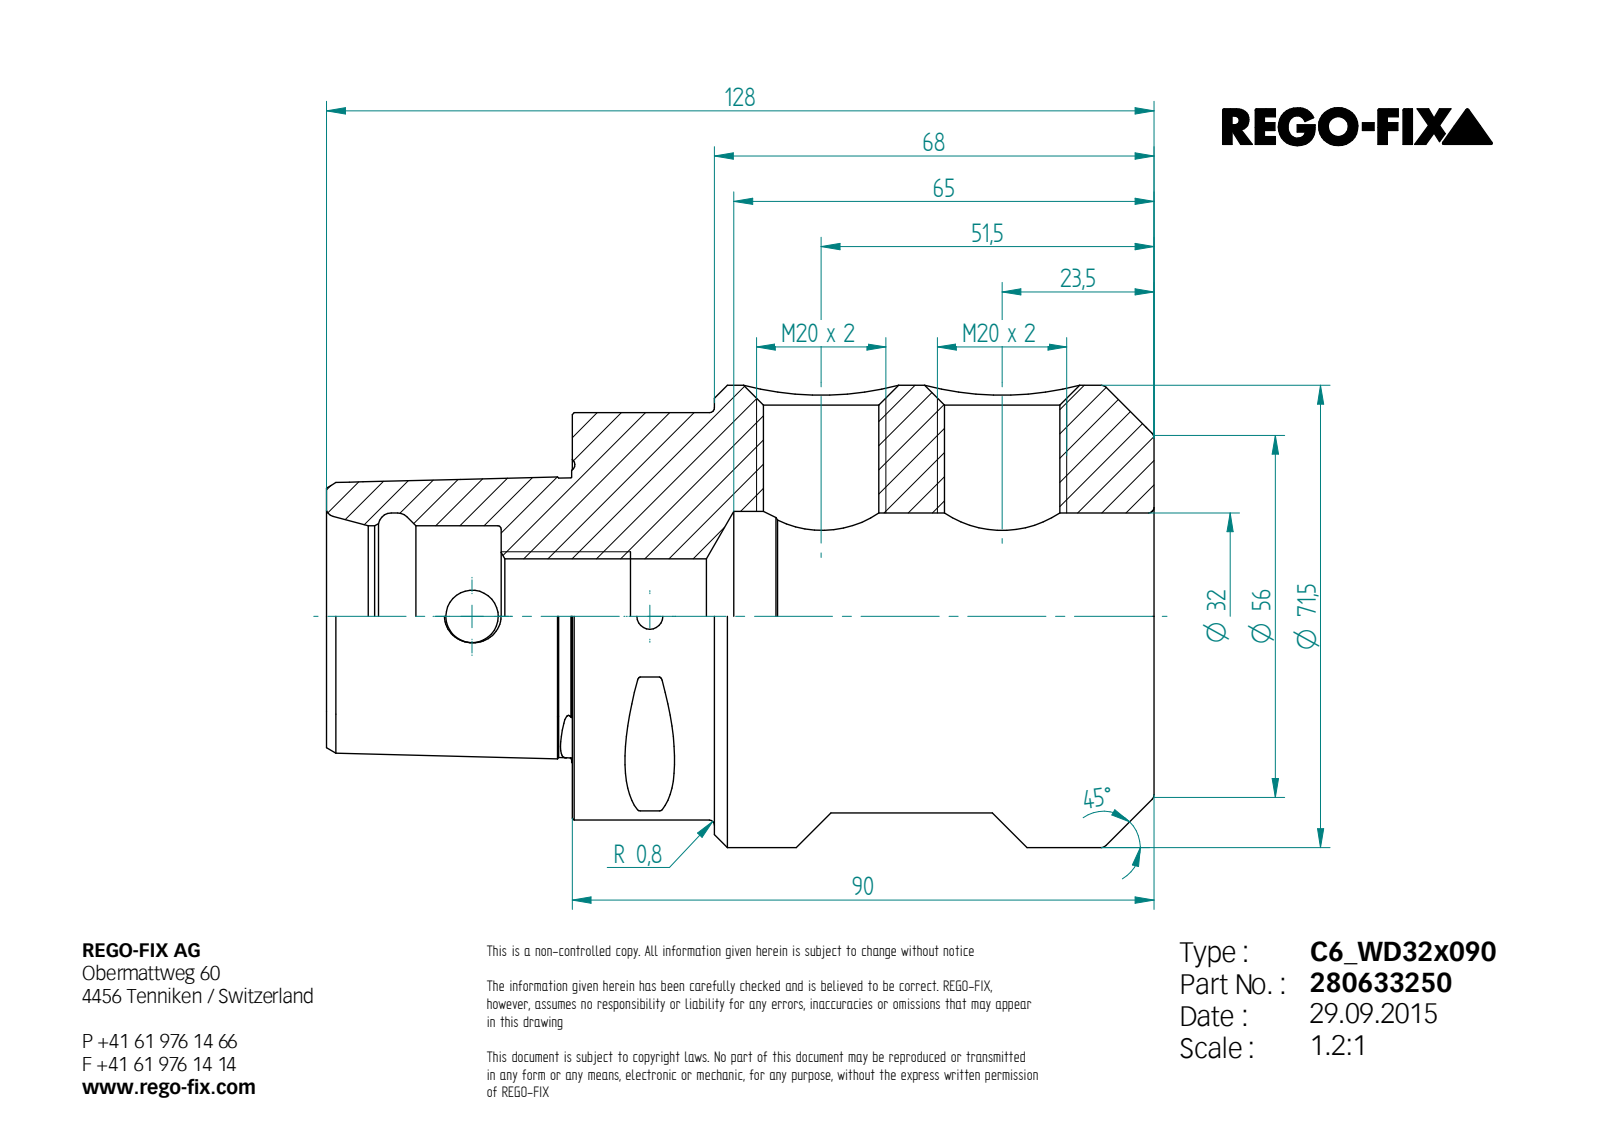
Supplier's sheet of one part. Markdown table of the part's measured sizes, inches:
| quantity | value |
| --- | --- |
| STEP written by | Unknown (AUTOMOTIVE_DESIGN) |
| units | inches |
| bodies | 1 solid, 112 faces (23 planar, 22 cylindrical, 67 other) |
| overall size | 5.039 × 2.815 × 2.815 |
| volume | 17.84 in³ |
| surface area | 66.93 in² |
| round holes (diameter × count) | 0.702 × 3, 0.157 × 1, 0.319 × 1, 1.102 × 1, 1.26 × 1, 1.28 × 1 |
| round bosses / shafts (diameter × count) | 2.815 × 1, 2.48 × 1 |
| partial cylindrical surfaces (radius × count) | 0.02 × 8 |
| main face-to-face distances | 3.543, 1.496, 5.039, 2.362, 0.866, 2.677, 0.98, 1.063, 0.433, 1.299 |
| hole center spacings | 1.083, 1.102 |
